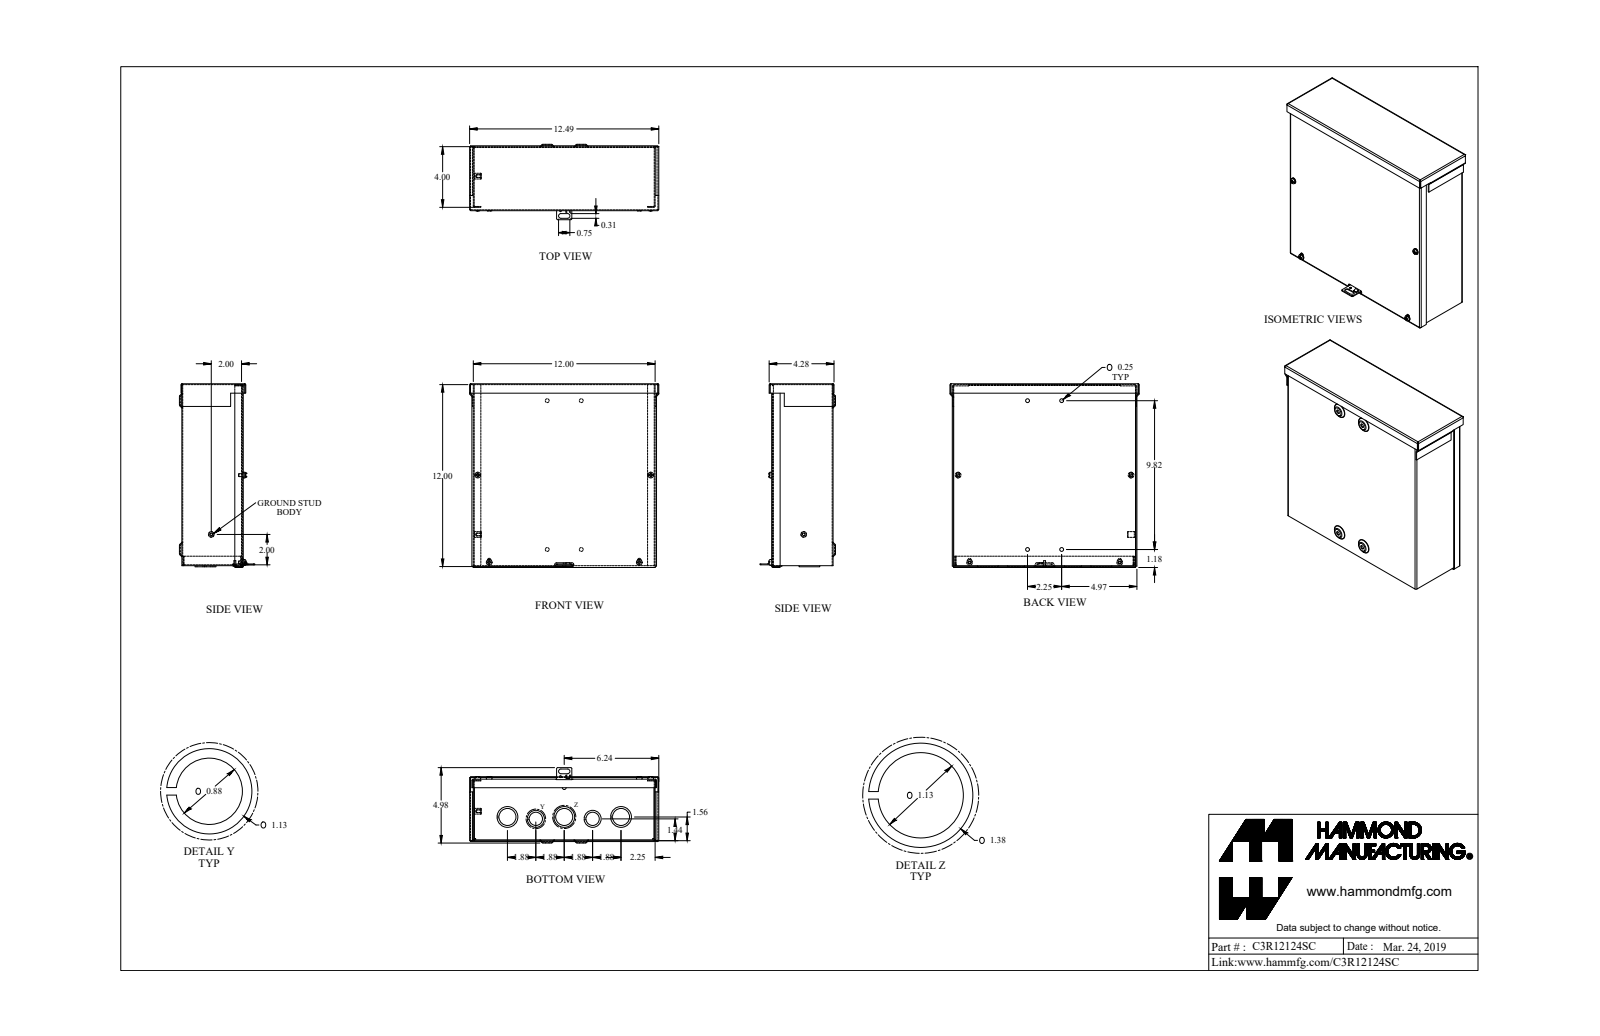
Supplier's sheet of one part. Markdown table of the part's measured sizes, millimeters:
| quantity | value |
| --- | --- |
| part name | C3R12124SC_Default |
| STEP written by | SolidWorks 2019 (CONFIG_CONTROL_DESIGN) |
| units | millimeters |
| bodies | 11 solids, 429 faces (226 planar, 117 cylindrical, 86 other) |
| overall size | 317.2 × 307.8 × 126.4 |
| volume | 523 400 mm³ |
| surface area | 728 400 mm² |
| round holes (diameter × count) | 4.3 × 4, 6.4 × 4, 28.6 × 3, 22.2 × 2, 3.2 × 1, 3.5 × 1, 4 × 1 |
| round bosses / shafts (diameter × count) | 4.8 × 4, 9.5 × 3, 34.9 × 2, 28.6 × 2, 9.5 × 2, 34.9 × 1, 3.2 × 1 |
| partial cylindrical surfaces (radius × count) | 0.7 × 21, 2.2 × 21, 2.8 × 8, 3.2 × 8, 4 × 2 |
| main face-to-face distances | 1.4, 101.6, 100.2, 103, 303.4, 304.8, 1.4, 301.9, 301.9, 303.4 |
| hole center spacings | 170.6, 213.7, 47.7, 47.8, 57.2, 70.8, 95.3, 99.6 |
